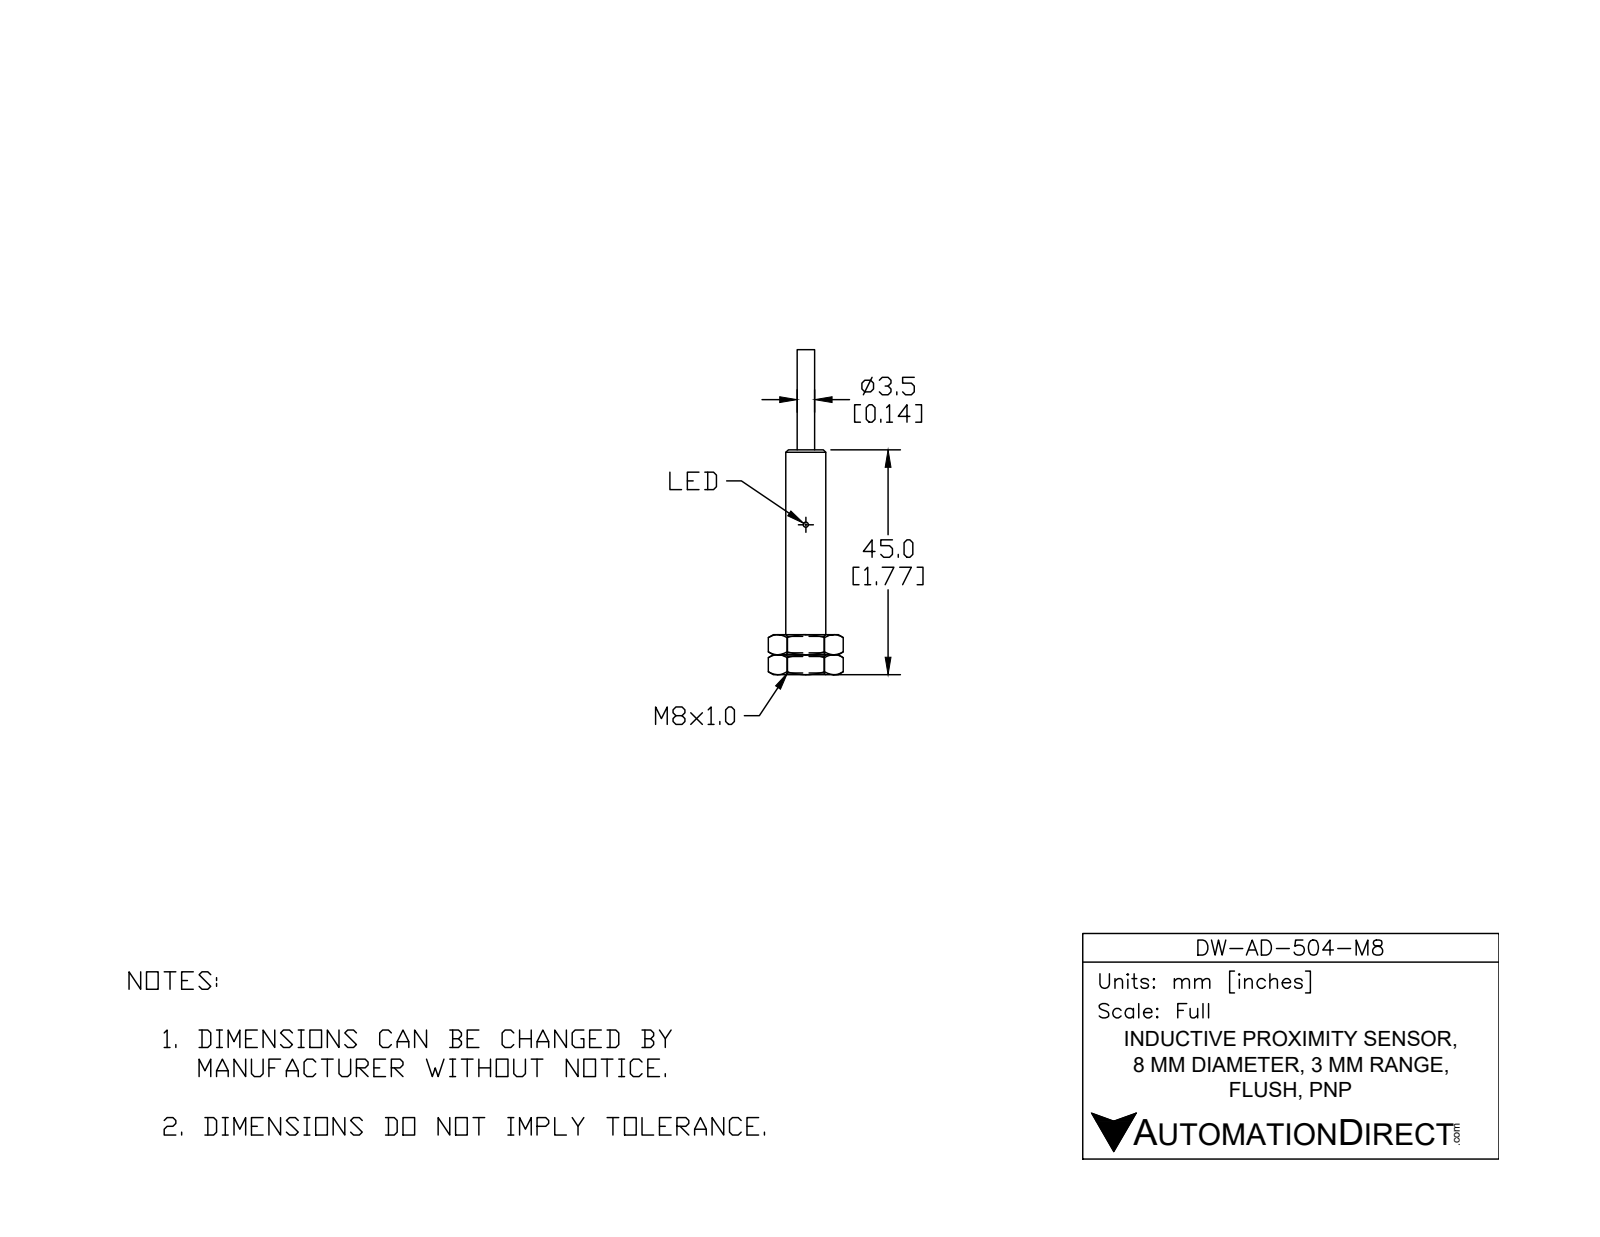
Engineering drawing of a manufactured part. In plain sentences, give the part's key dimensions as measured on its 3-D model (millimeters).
The part is named "DW-AD-504-M8". Its 3-D file was written by "SolidWorks 2017 (AUTOMOTIVE_DESIGN)". It is 1 solid with 10 faces: 4 planar, 3 cylindrical and 3 other. Overall it measures 71.2 by 8 by 8 millimeters. Its volume is 2 790 cubic millimeters and its surface area 1 632 square millimeters. Round bosses or shafts: 1 of diameter 8, 1 of diameter 6.5, 1 of diameter 5. The main face-to-face distances are 71.2, 45.5, 25.7, 45, 0.5, 26.2.
